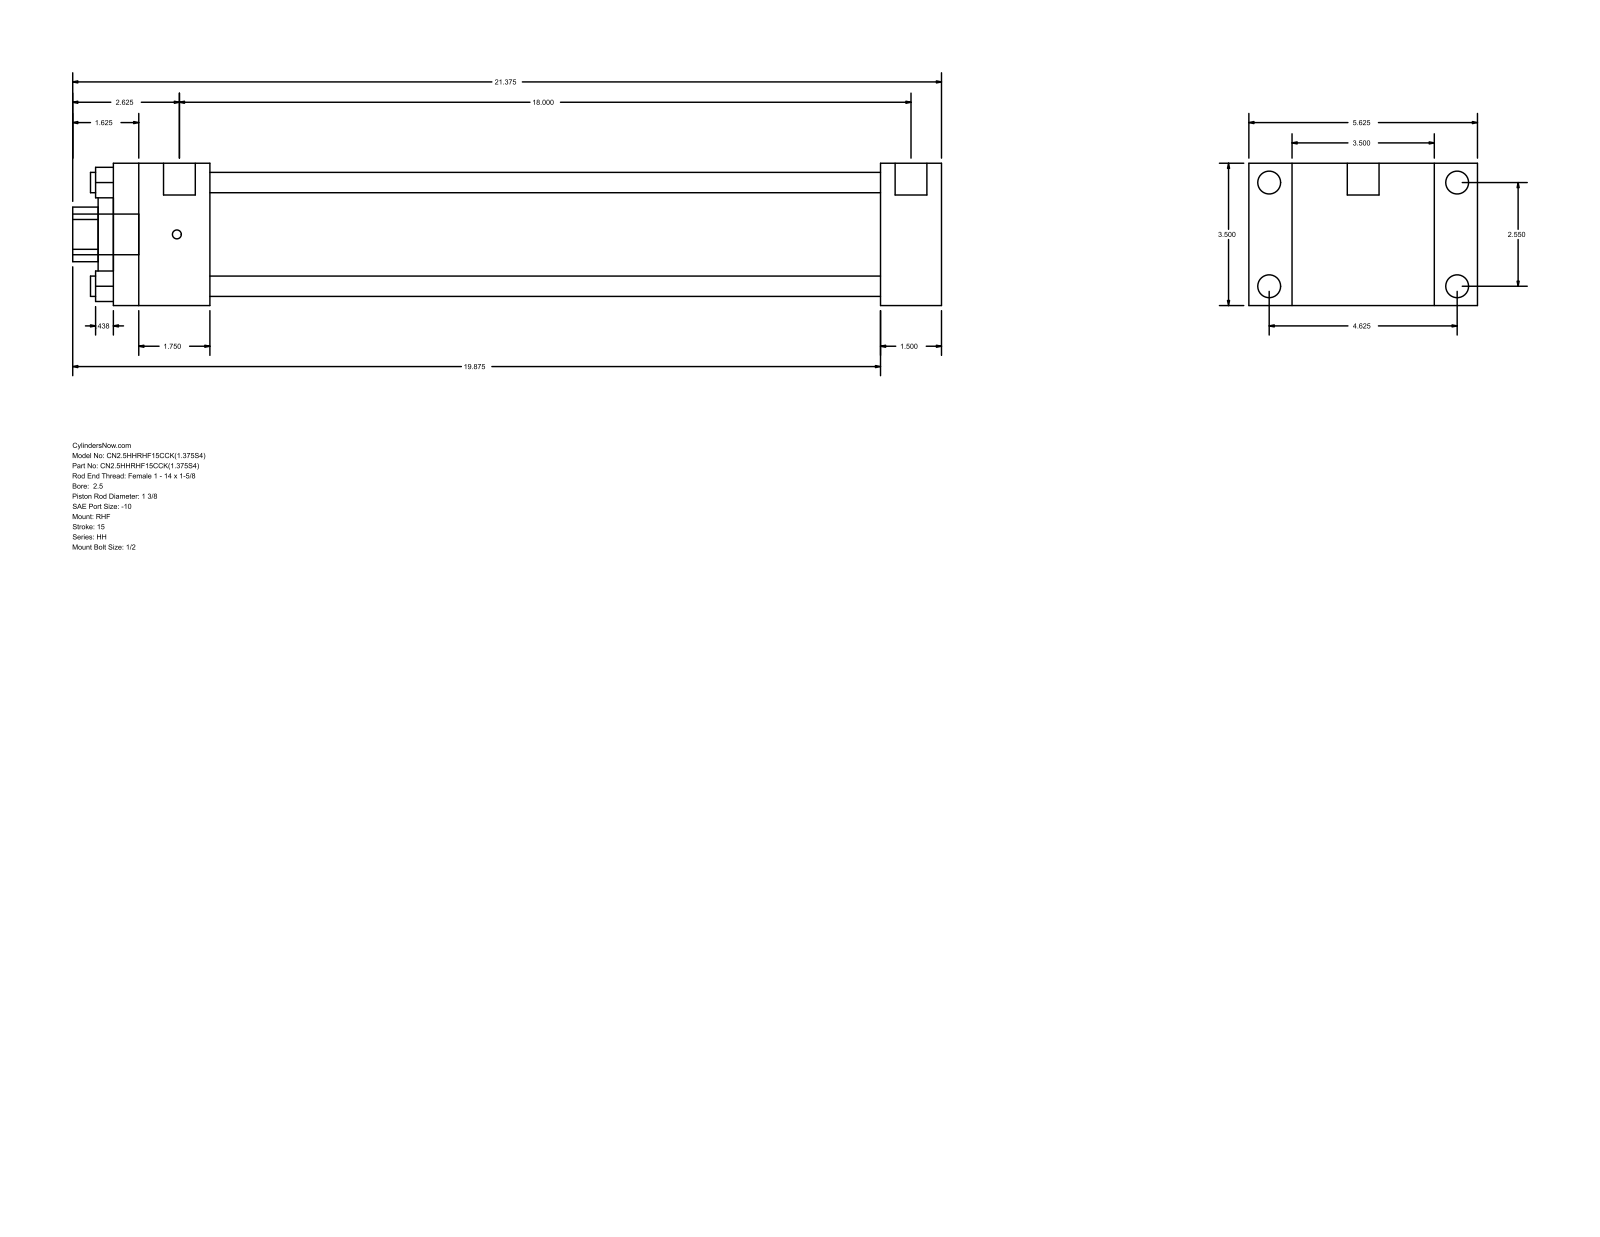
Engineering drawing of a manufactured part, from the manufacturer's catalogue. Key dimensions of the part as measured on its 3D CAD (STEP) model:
Part name (STEP PRODUCT): HH_RHF__0250_1.375
STEP written by: GSSL Pune (CONFIG_CONTROL_DESIGN)
Units: millimetres
Bodies: 0 solids, 88 faces (60 planar, 28 cylindrical, 0 other)
Overall size (bounding box): 542.92 × 142.88 × 88.9
Round holes (diameter × count): ⌀12.7 ×4, ⌀34.92 ×1, ⌀50.8 ×1, ⌀73.03 ×1
Round bosses / shafts (diameter × count): ⌀14.3 ×4, ⌀5.56 ×4, ⌀19.84 ×2, ⌀25.4 ×1
Partial cylindrical surfaces — rounded edges, fillets, slot ends (radius × count): R17.06 ×1
Main face-to-face distances: 88.9, 38.1, 26.99, 115.89, 479.42, 517.52, 142.88, 60.32, 419.1, 457.2
Hole centre spacings: 45.79, 64.76, 91.58
